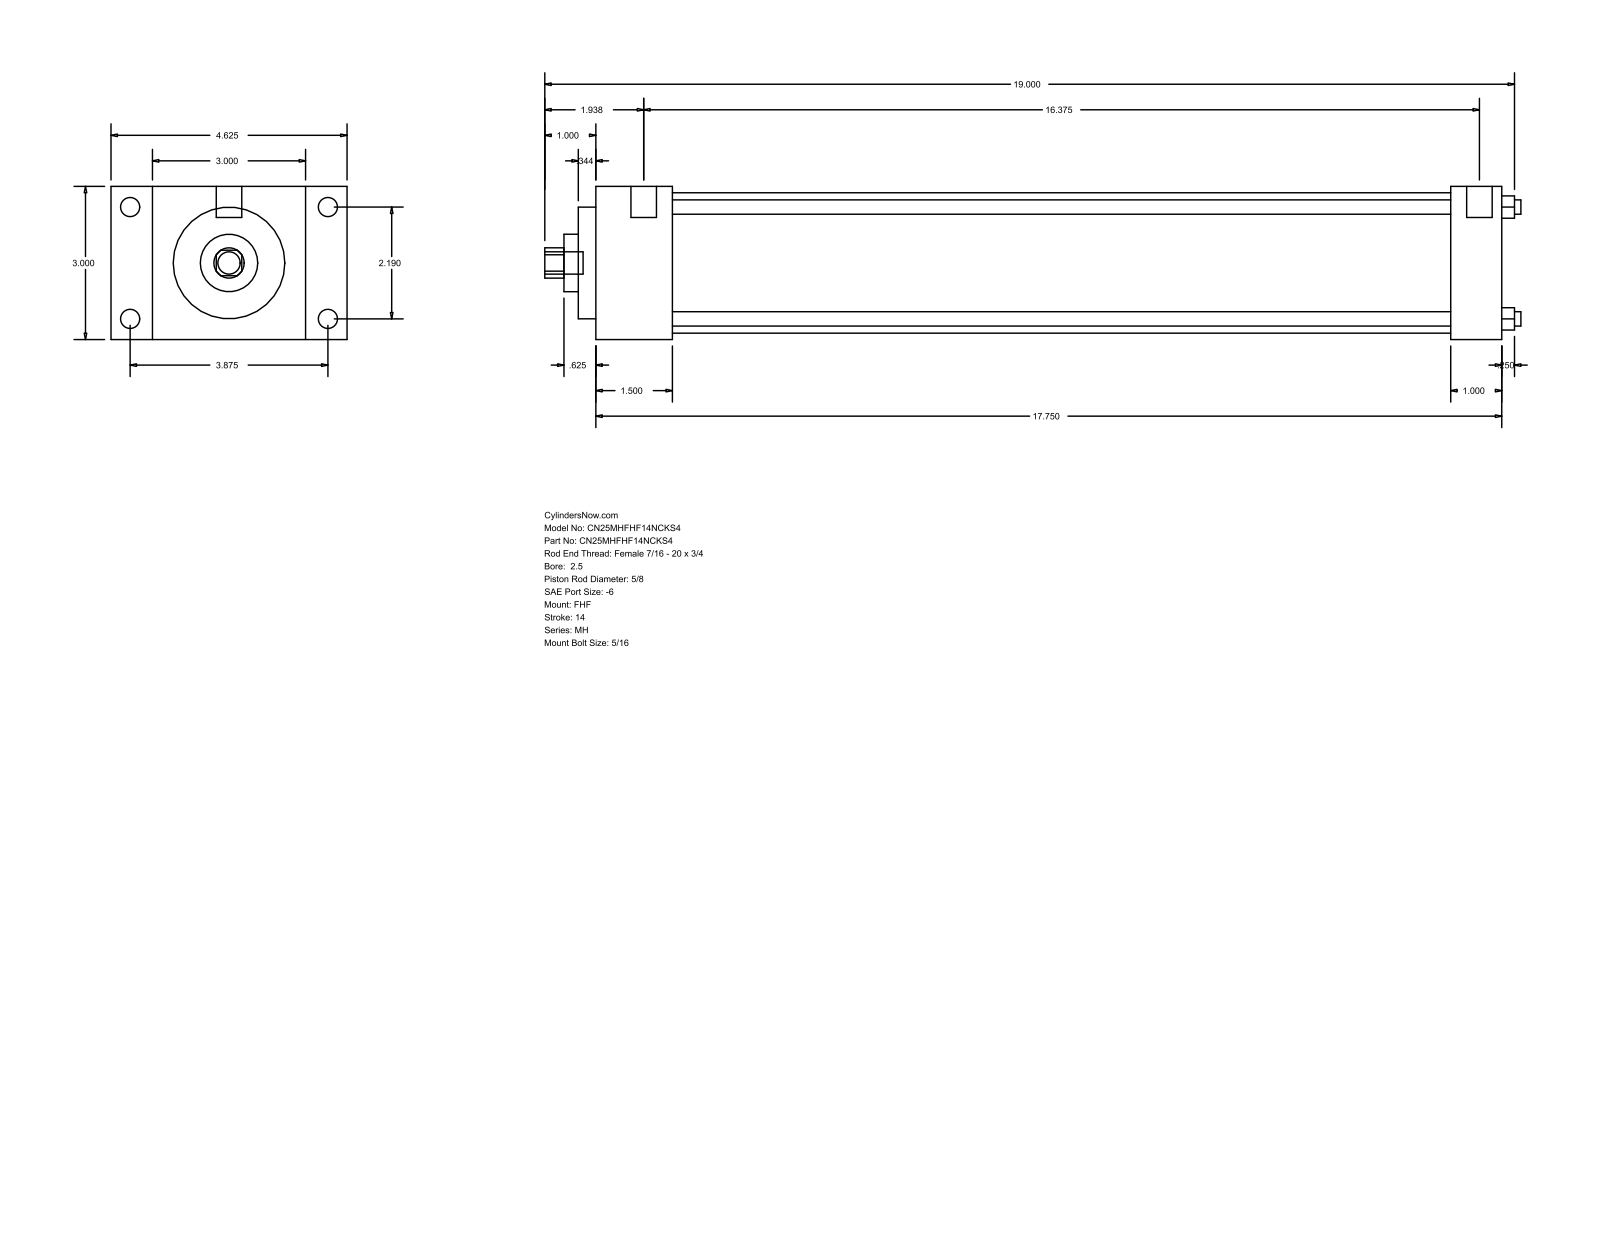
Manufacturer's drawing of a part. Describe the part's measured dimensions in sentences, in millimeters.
The part is named "MH_FHF__0250_0.625". Its 3-D file was written by "GSSL Pune (CONFIG_CONTROL_DESIGN)". It is 0 solids with 90 faces: 61 planar, 29 cylindrical and 0 other. Overall it measures 485.77 by 117.47 by 76.2 millimeters. Round holes: 4 of diameter 7.14, 1 of diameter 15.88, 1 of diameter 28.57, 1 of diameter 55.55, 1 of diameter 69.85. Round bosses or shafts: 4 of diameter 9.53, 4 of diameter 5.56, 2 of diameter 12.7, 1 of diameter 11.11. Partial cylindrical surfaces (rounded edges, fillets, slot ends): 1 of radius 7.54. The main face-to-face distances are 76.2, 450.85, 38.1, 412.75, 20.64, 96.84, 117.48, 25.4, 425.45, 387.35. The hole center spacings are 39.33, 55.62, 78.66.
